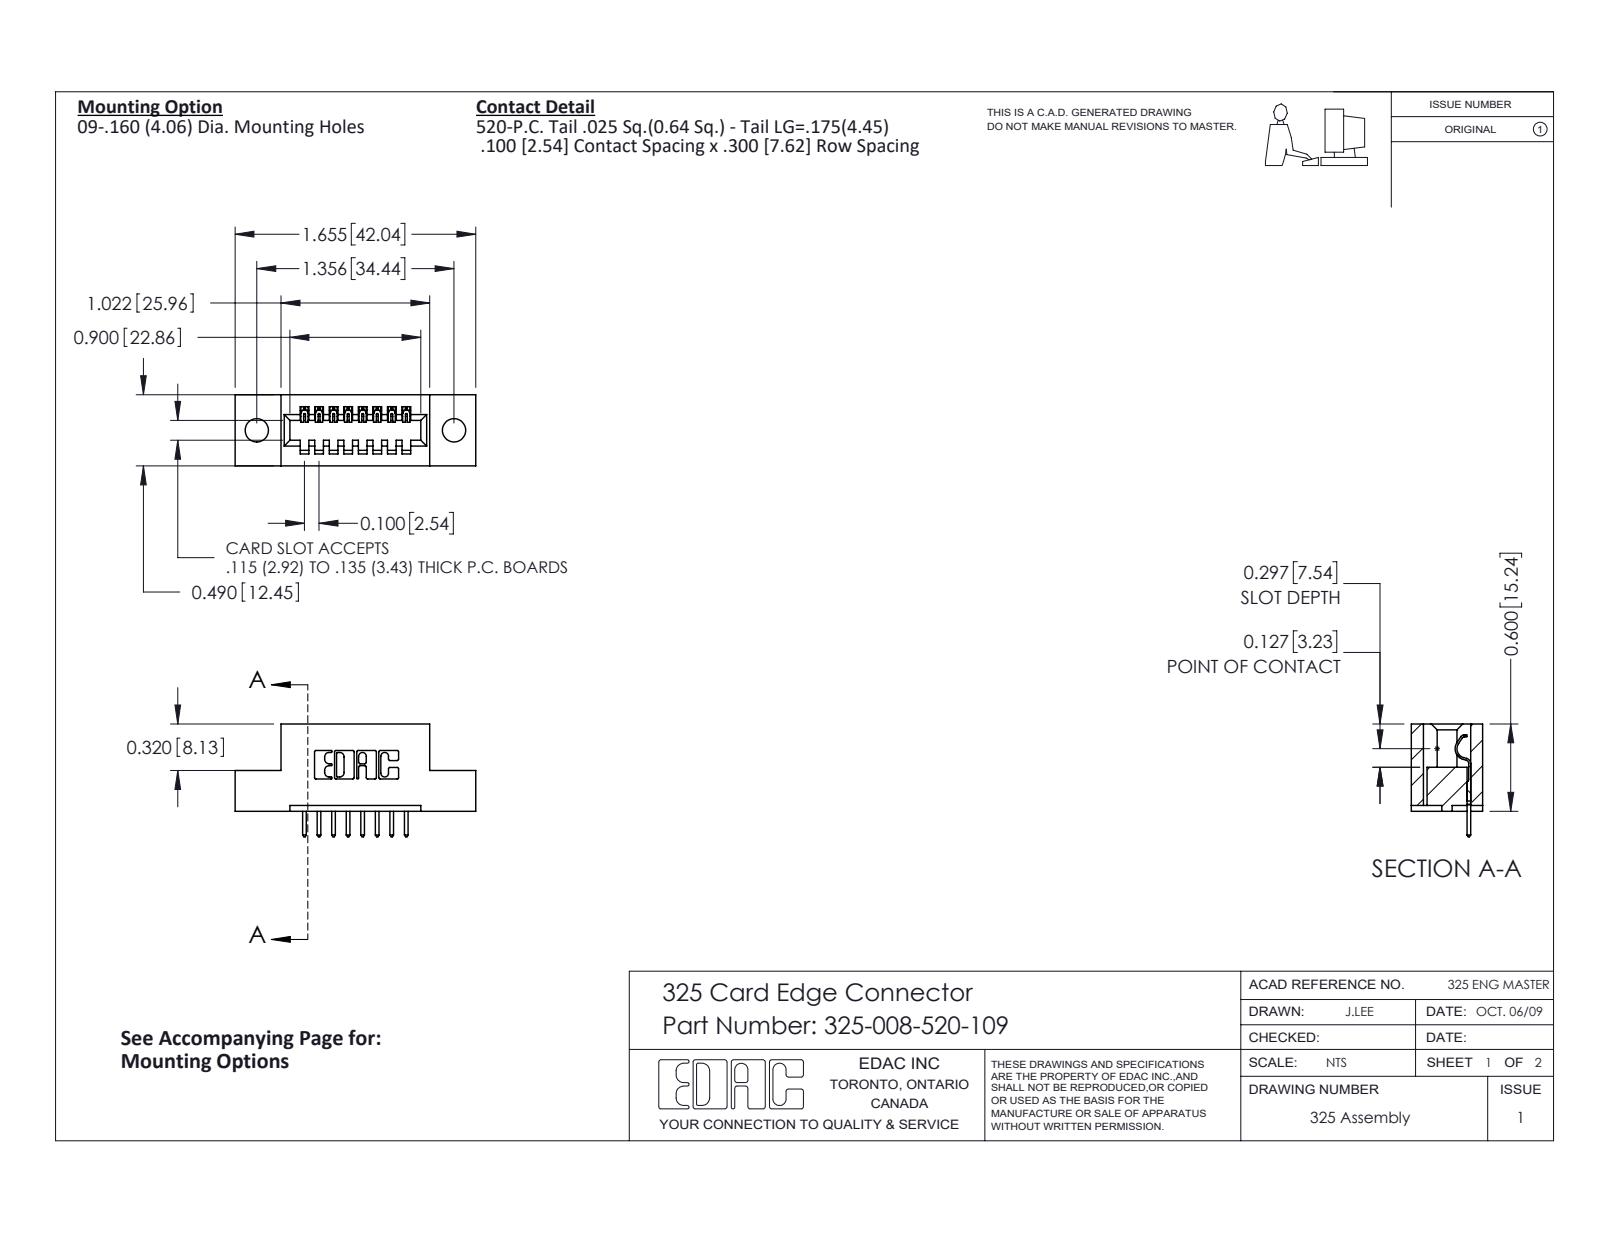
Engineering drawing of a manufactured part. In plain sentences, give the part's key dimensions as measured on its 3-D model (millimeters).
The part is named "325-008-520-109; 325 Part_.160 TH; 325-292-001_325-293-120". Its 3-D file was written by "SolidWorks 2016 (CONFIG_CONTROL_DESIGN)". It is 9 solids with 578 faces: 406 planar, 172 cylindrical and 0 other. Overall it measures 42 by 19.7 by 12.4 millimeters. Its volume is 4 820 cubic millimeters and its surface area 4 498 square millimeters. Round holes: 2 of diameter 4.1. Partial cylindrical surfaces (rounded edges, fillets, slot ends): 22 of radius 0.3, 16 of radius 0.2, 16 of radius 0.3, 6 of radius 0.2, 6 of radius 0.8, 3 of radius 0.7, 1 of radius 0.4, 1 of radius 0.6. The main face-to-face distances are 7.6, 2.5, 5.1, 1, 12.4, 2.1, 10.3, 10.2, 1.5, 15.2. The hole center spacings are 34.4.
